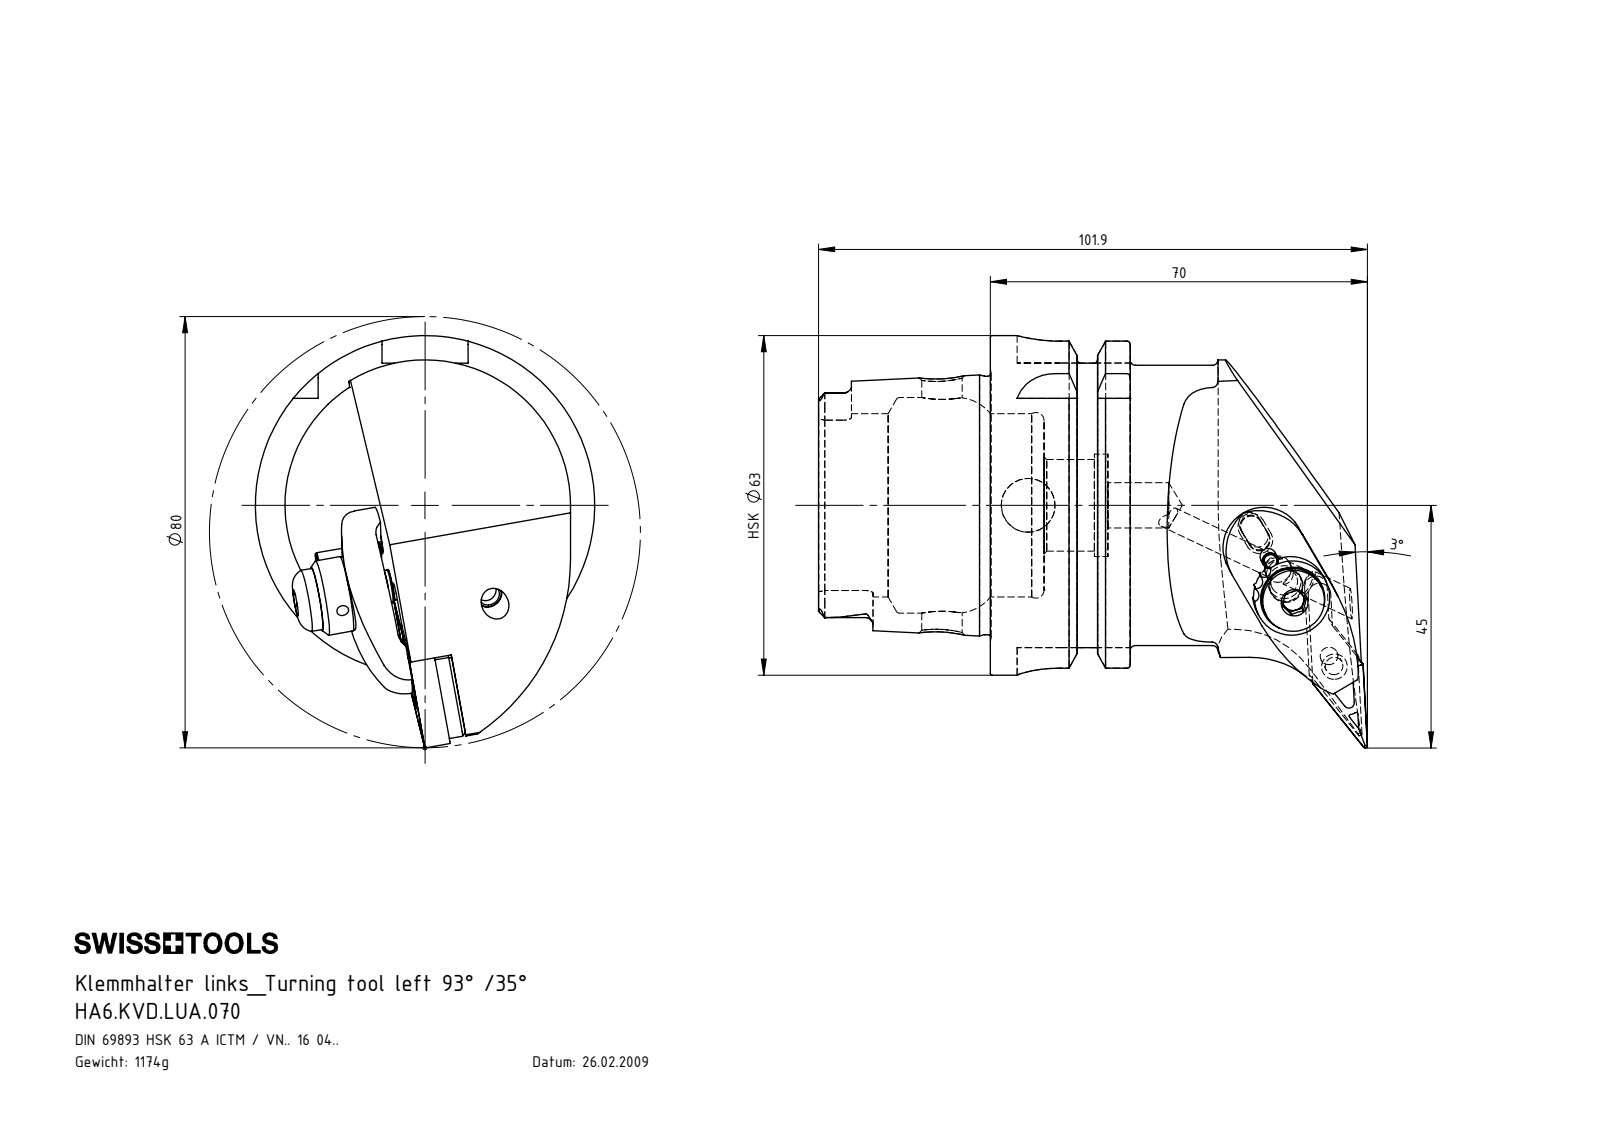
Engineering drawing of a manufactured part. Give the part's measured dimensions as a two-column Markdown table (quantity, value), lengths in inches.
| quantity | value |
| --- | --- |
| part name | HA6.KVD.LUA.070; WCB-ER2.001.009_A; KVT_MB_600_050; VNMG160404 (+6 more) |
| STEP written by | SolidWorks 2017 (AUTOMOTIVE_DESIGN) |
| units | inches |
| bodies | 12 solids, 475 faces (133 planar, 157 cylindrical, 185 other) |
| overall size | 4.012 × 3.012 × 2.48 |
| volume | 9.097 in³ |
| surface area | 54.53 in² |
| round holes (diameter × count) | 0.079 × 3, 0.197 × 2, 0.276 × 2, 0.094 × 1, 0.118 × 1, 0.13 × 1, 0.15 × 1, 0.157 × 1, 0.165 × 1, 0.195 × 1, 0.272 × 1, 0.295 × 1 |
| round bosses / shafts (diameter × count) | 0.157 × 2, 0.118 × 2, 2.48 × 1, 2.163 × 1, 2.047 × 1, 1.887 × 1, 0.551 × 1, 0.453 × 1 |
| partial cylindrical surfaces (radius × count) | 0.013 × 6, 0.023 × 6, 0.055 × 6, 0.016 × 4, 0.315 × 4, 0.059 × 3, 0.02 × 2, 0.079 × 2 |
| main face-to-face distances | 1.022, 0.63, 0.392, 1.256, 1.648, 2.278, 0.051, 2.079, 0.858, 0.3 |
| hole center spacings | 0.316, 0.323, 0.753, 0.759, 1.075, 1.076 |
